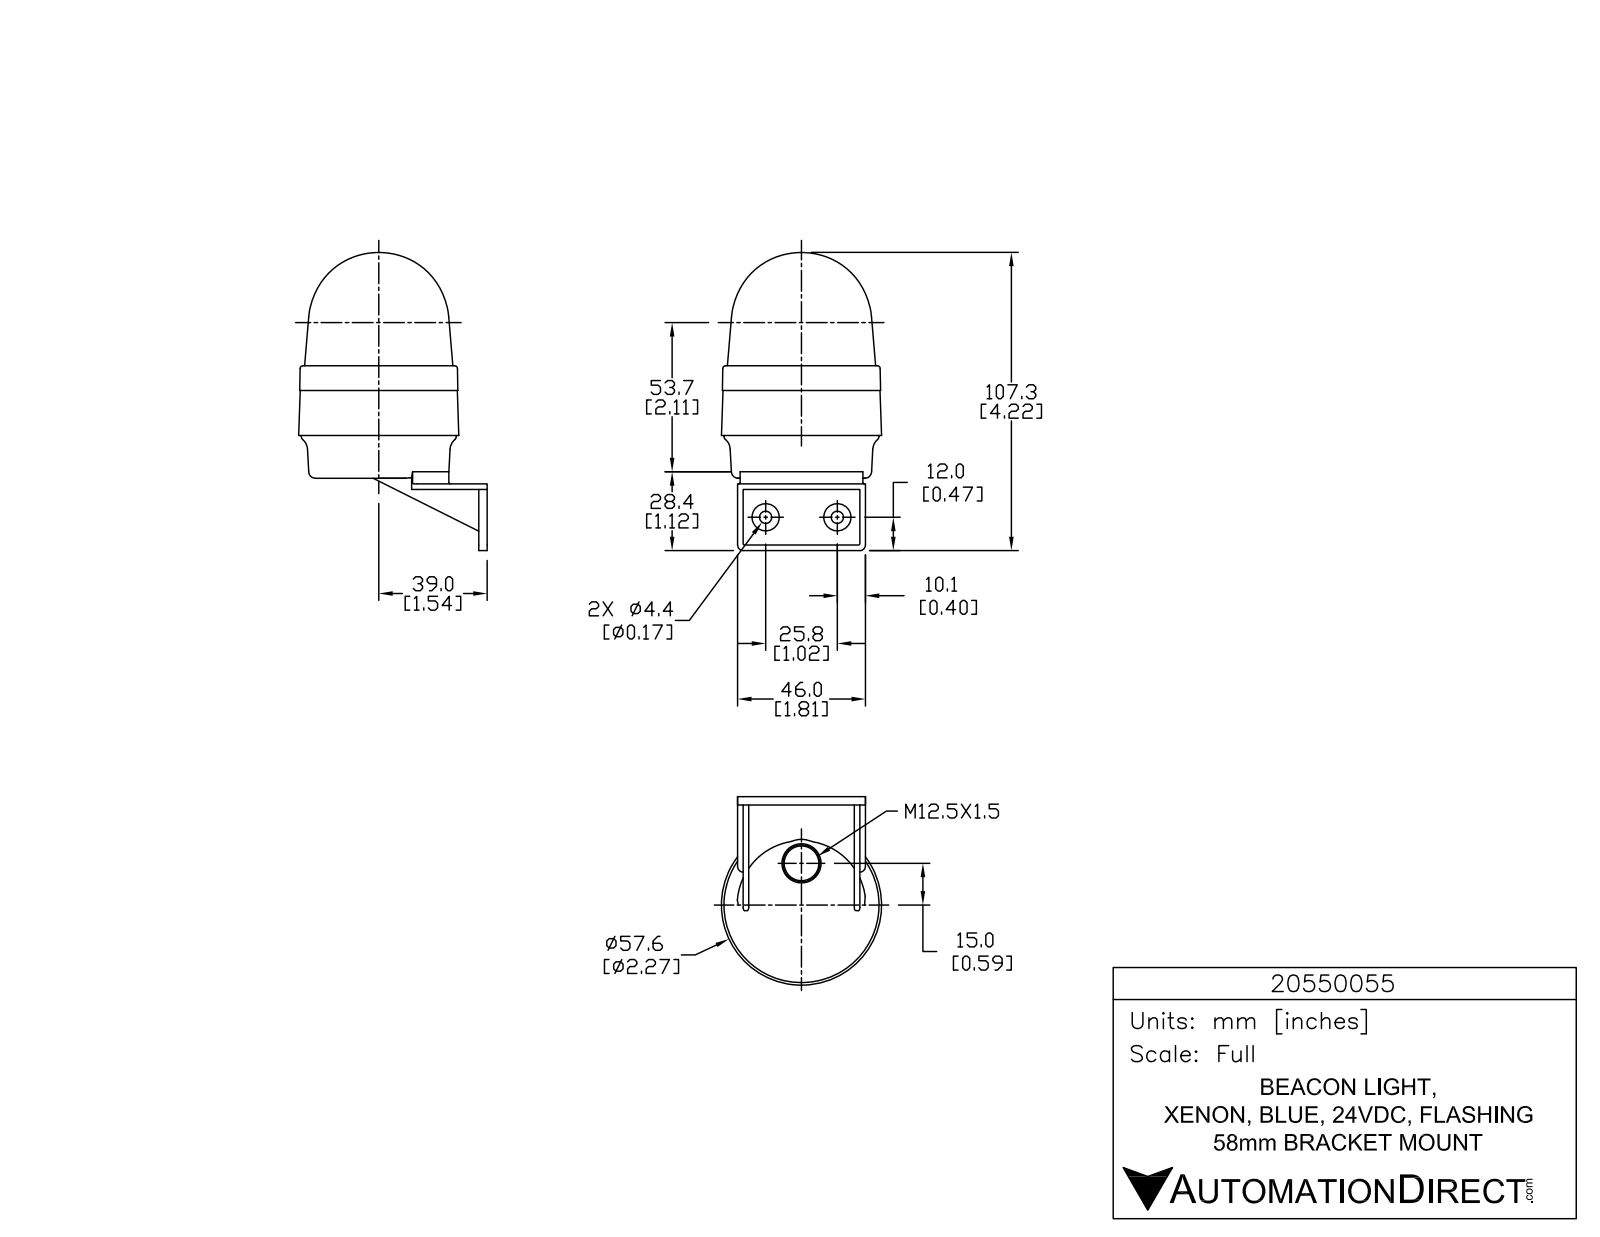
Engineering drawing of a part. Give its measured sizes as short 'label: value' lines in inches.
name: 20550055
written by: SolidWorks 2015 (AUTOMOTIVE_DESIGN)
unit: in
bodies: 1 solid, 828 faces (551 planar, 179 cylindrical, 98 other)
size: 4.225 × 2.852 × 2.407
volume: 10.27 in³; area: 33.38 in²
holes: 3× ⌀0.039, 2× ⌀0.173
bosses: 3× ⌀0.226, 3× ⌀0.056, 2× ⌀0.386, 1× ⌀2.197
rounds: 6× R0.008, 6× R0.008, 6× R0.008, 6× R0.02, 6× R0.131, 4× R0.079, 3× R0.004, 3× R0.005
face distances: 0.079, 0.157, 1.575, 1.654, 0.039, 0.118, 1.496, 0.866, 0.945, 0.764
hole spacings: 1.016
